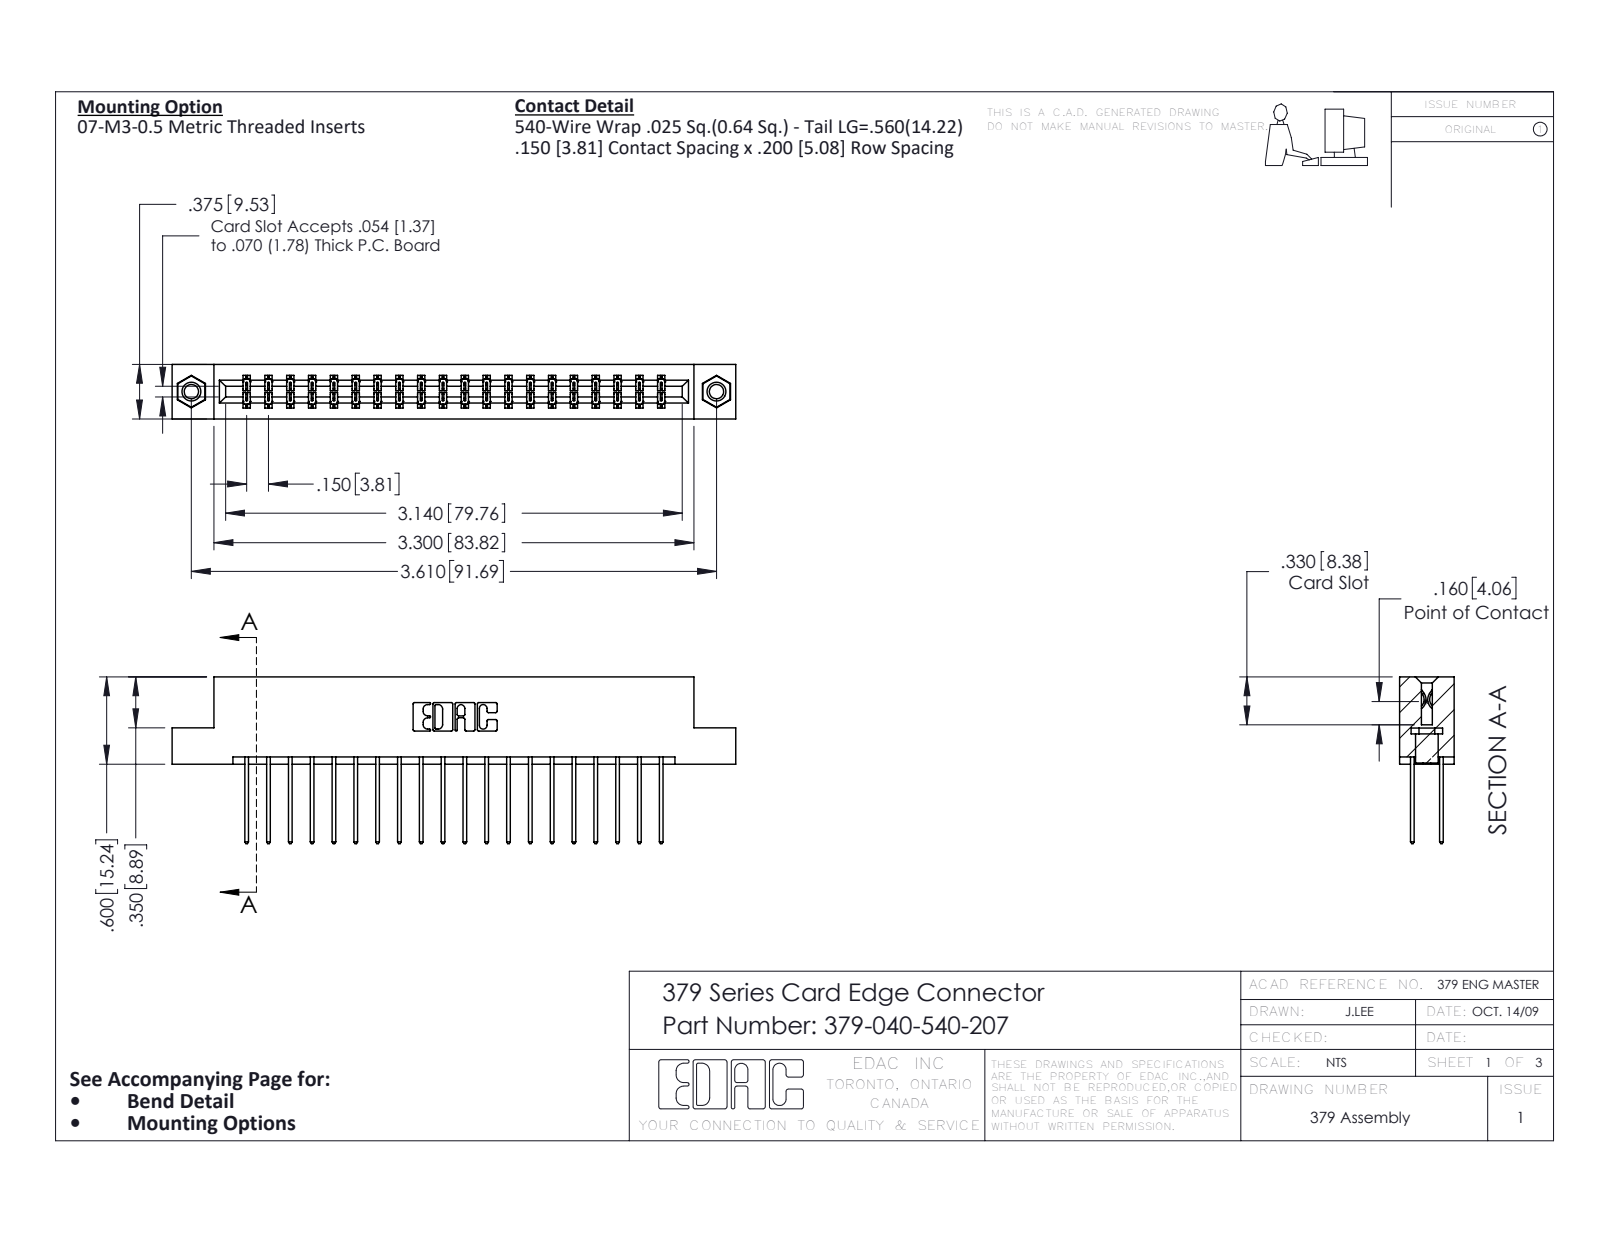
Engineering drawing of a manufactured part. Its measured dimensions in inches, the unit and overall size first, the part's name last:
Units: inches
Overall size (bounding box): 3.875 × 1.147 × 0.375
Round holes (diameter × count): ⌀0.098 ×2, ⌀0.125 ×2, ⌀0.156 ×2
Round bosses / shafts (diameter × count): ⌀0.155 ×2
Partial cylindrical surfaces — rounded edges, fillets, slot ends (radius × count): R0.006 ×60, R0.01 ×40, R0.01 ×22, R0.007 ×6, R0.031 ×6, R0.026 ×3, R0.014 ×2, R0.022 ×2
Main face-to-face distances: 0.3, 0.075, 0.2, 0.375, 0.1, 0.275, 0.025, 0.076, 0.15, 0.225
Hole centre spacings: 3.61
Volume: 0.631 in³ · Surface area: 18.92 in²
Bodies: 43 solids, 2254 faces (1542 planar, 696 cylindrical, 16 other)
Part name (STEP PRODUCT): 345-292-001_345-293-140; 379-040-540-207; 345-250-001_345-250-005-103; 379 Part_Flush - .156 Dia - TI
STEP written by: SolidWorks 2016 (CONFIG_CONTROL_DESIGN)
